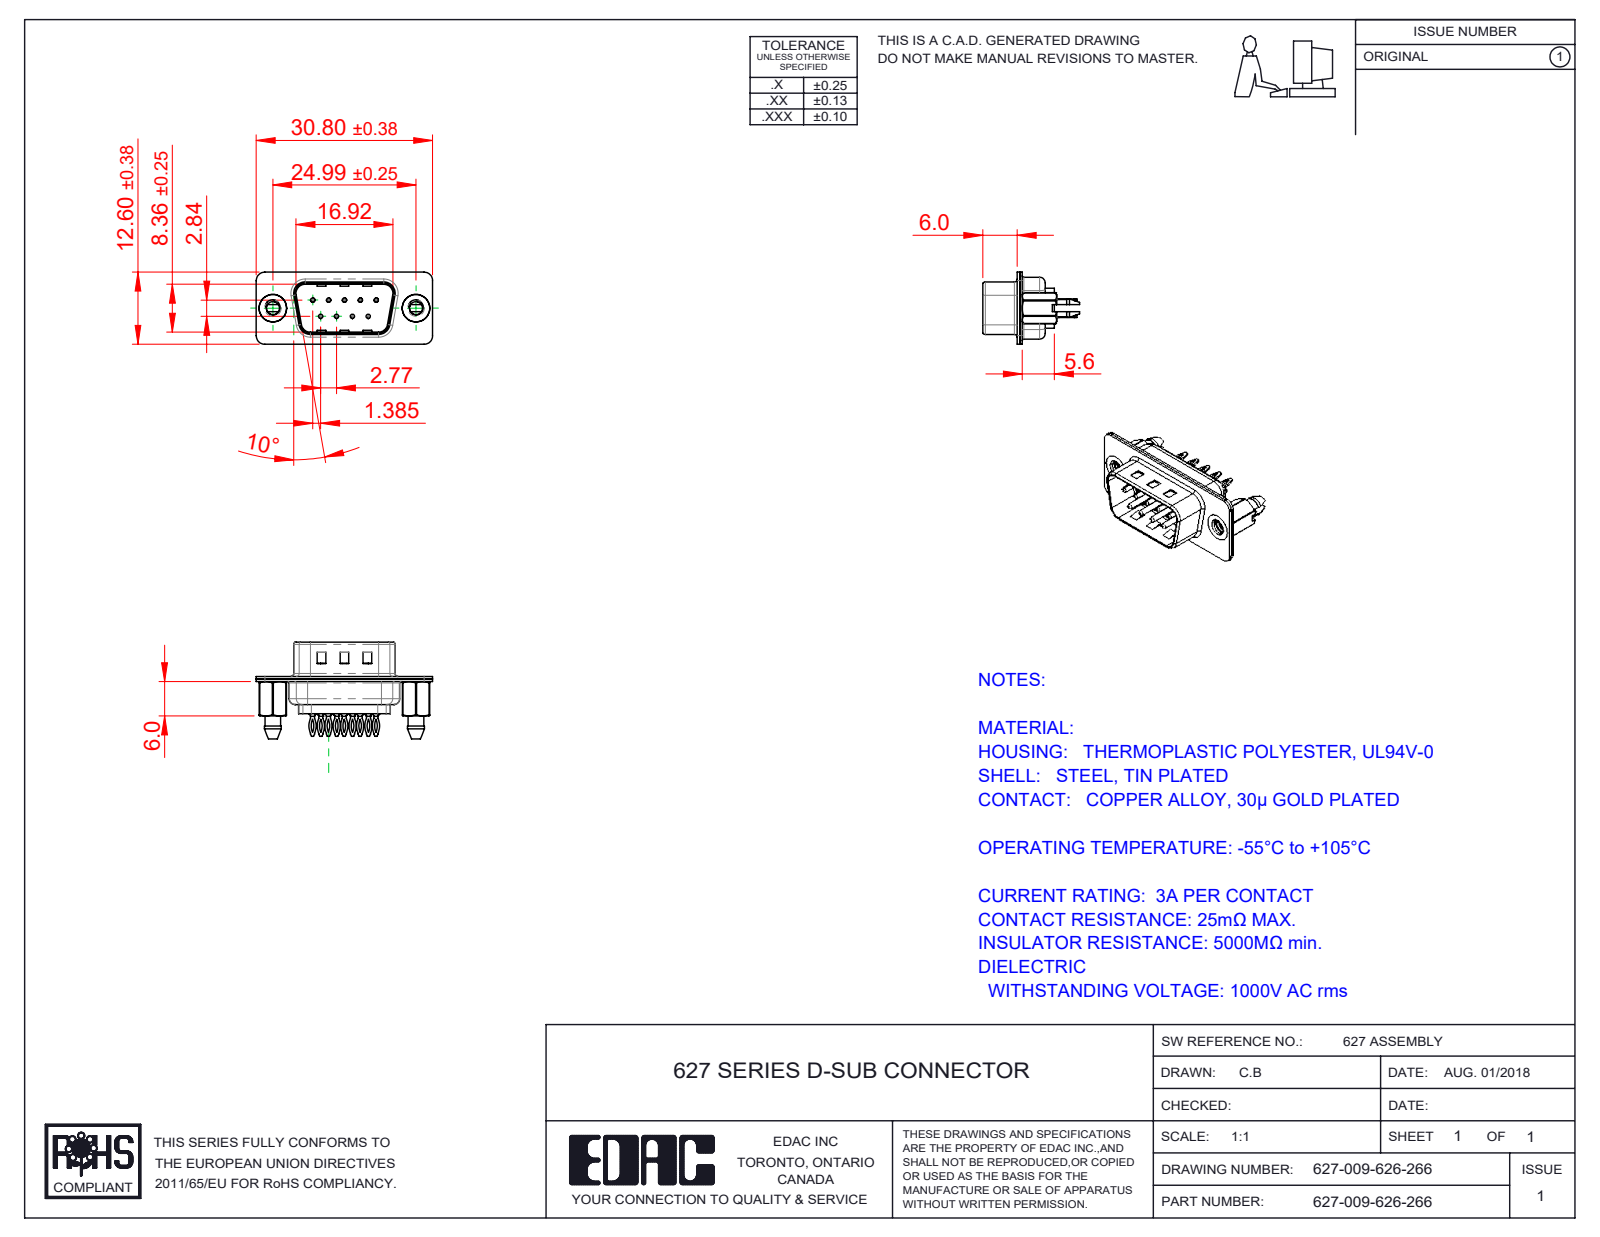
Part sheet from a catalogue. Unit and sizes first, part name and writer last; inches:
Units: inches
Overall size (bounding box): 1.213 × 0.665 × 0.496
Round holes (diameter × count): ⌀0.014 ×9, ⌀0.043 ×9, ⌀0.063 ×9, ⌀0.089 ×2, ⌀0.157 ×2, ⌀0.189 ×2
Round bosses / shafts (diameter × count): ⌀0.079 ×9, ⌀0.059 ×9, ⌀0.03 ×9, ⌀0.193 ×2
Partial cylindrical surfaces — rounded edges, fillets, slot ends (radius × count): R0.059 ×20, R0.115 ×18, R0.131 ×18, R0.079 ×12, R0.063 ×10, R0.02 ×8, R0.01 ×4, R0.024 ×4
Main face-to-face distances: 0.016, 0.018, 0.035, 0.032, 0.377, 0.055, 0.345, 0.256, 0.02, 0.059
Hole centre spacings: 0.124, 0.109, 0.218, 0.198, 0.198, 0.327, 0.294, 0.295
Volume: 0.087 in³ · Surface area: 6.505 in²
Bodies: 14 solids, 1062 faces (319 planar, 440 cylindrical, 303 other)
Part name (STEP PRODUCT): 627 Contact Row 2_26L; 627 4-40 Threaded Boardlock_LP; 627 Shell Rear_09 Contacts; 627 Contact Row 1_26L (+3 more)
STEP written by: SolidWorks 2020 (CONFIG_CONTROL_DESIGN)
